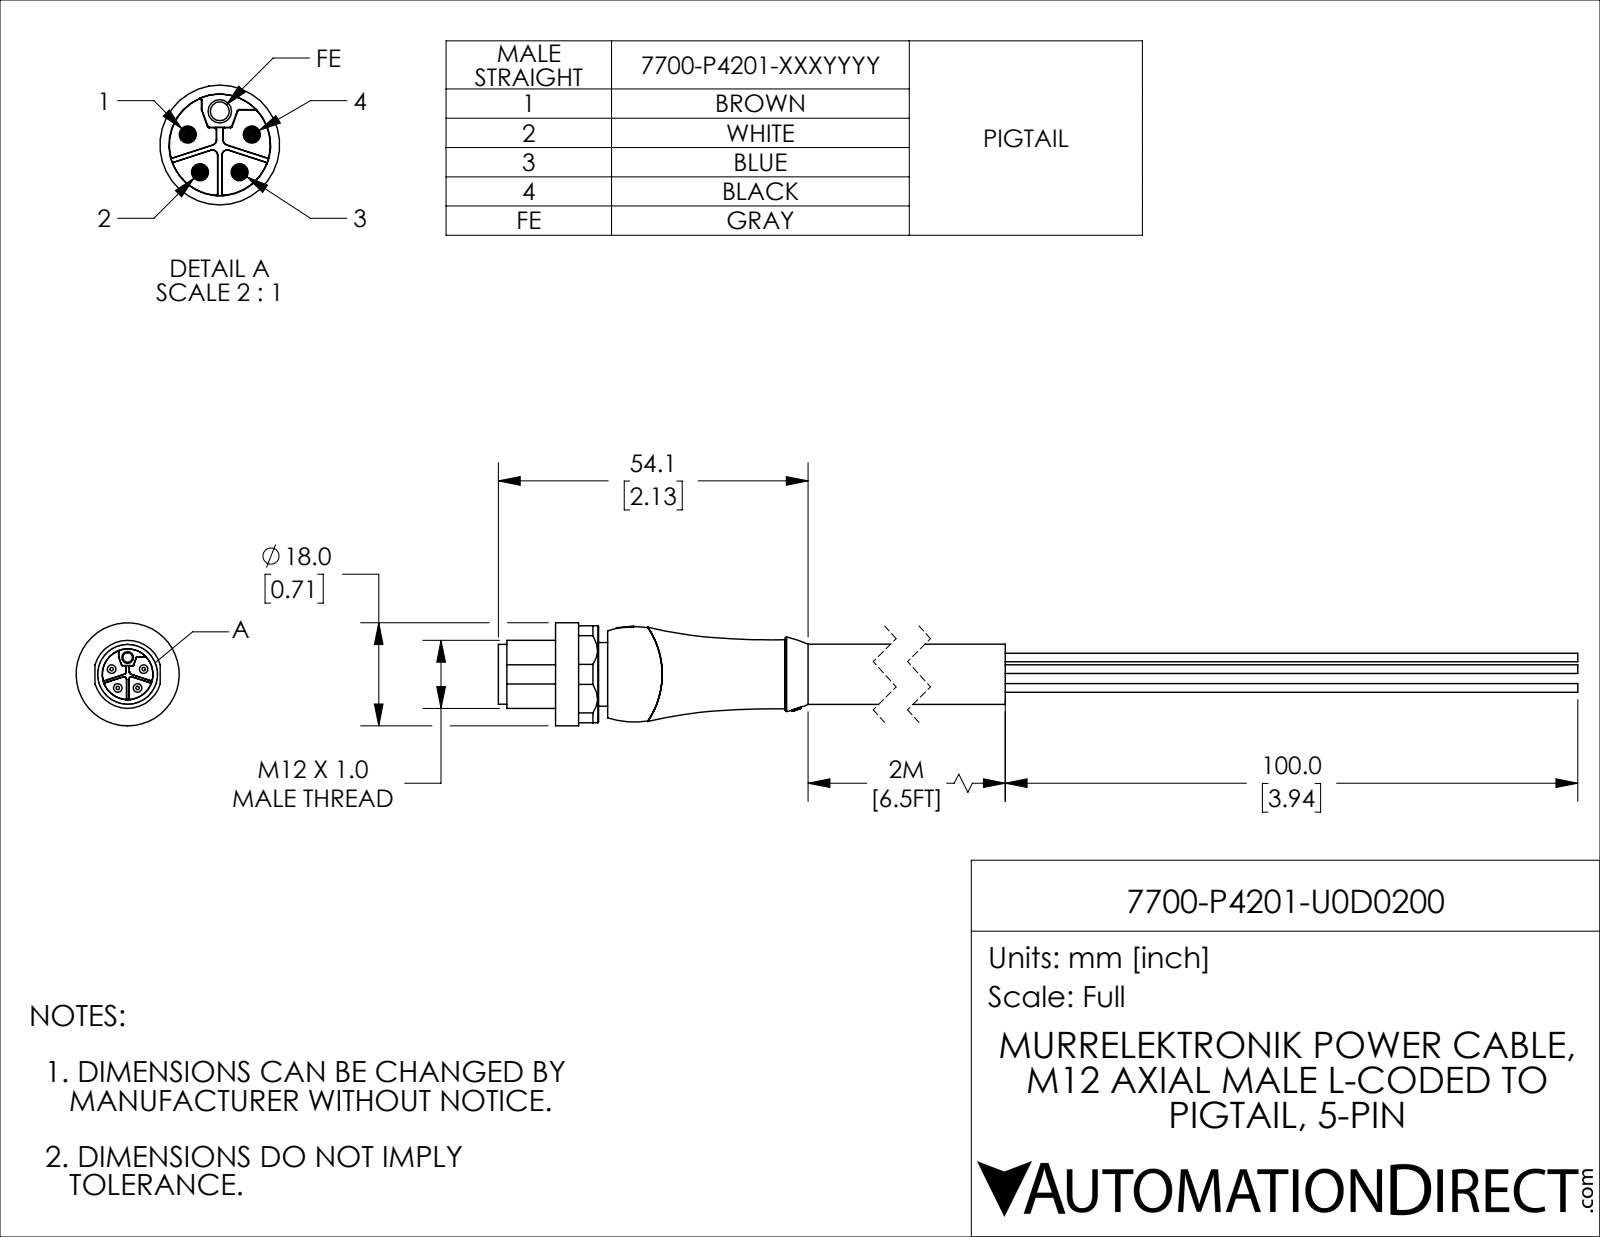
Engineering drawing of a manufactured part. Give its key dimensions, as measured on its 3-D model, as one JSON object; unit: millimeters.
{"part_name": "7700-P4201-U0D0200", "step_written_by": "SolidWorks 2021 (CONFIG_CONTROL_DESIGN)", "units": "millimeters", "bodies": {"solids": 1, "faces": 190, "planar": 87, "cylindrical": 51, "other": 52}, "overall_size": [254.1, 18, 18], "volume_mm3": 17489, "surface_area_mm2": 9110, "round_holes": [[1.65, 1]], "round_bosses_or_shafts": [[1.5, 5], [18, 1], [11.88, 1], [11.1, 1], [10.5, 1], [10.45, 1]], "partial_cylinders_radius": [[0.15, 6], [1.13, 1], [8.95, 1]], "face_to_face_distances": [9.1, 1.9, 7.2, 144.1, 136.9, 135, 16.94, 1.2, 8.4, 10.3]}
